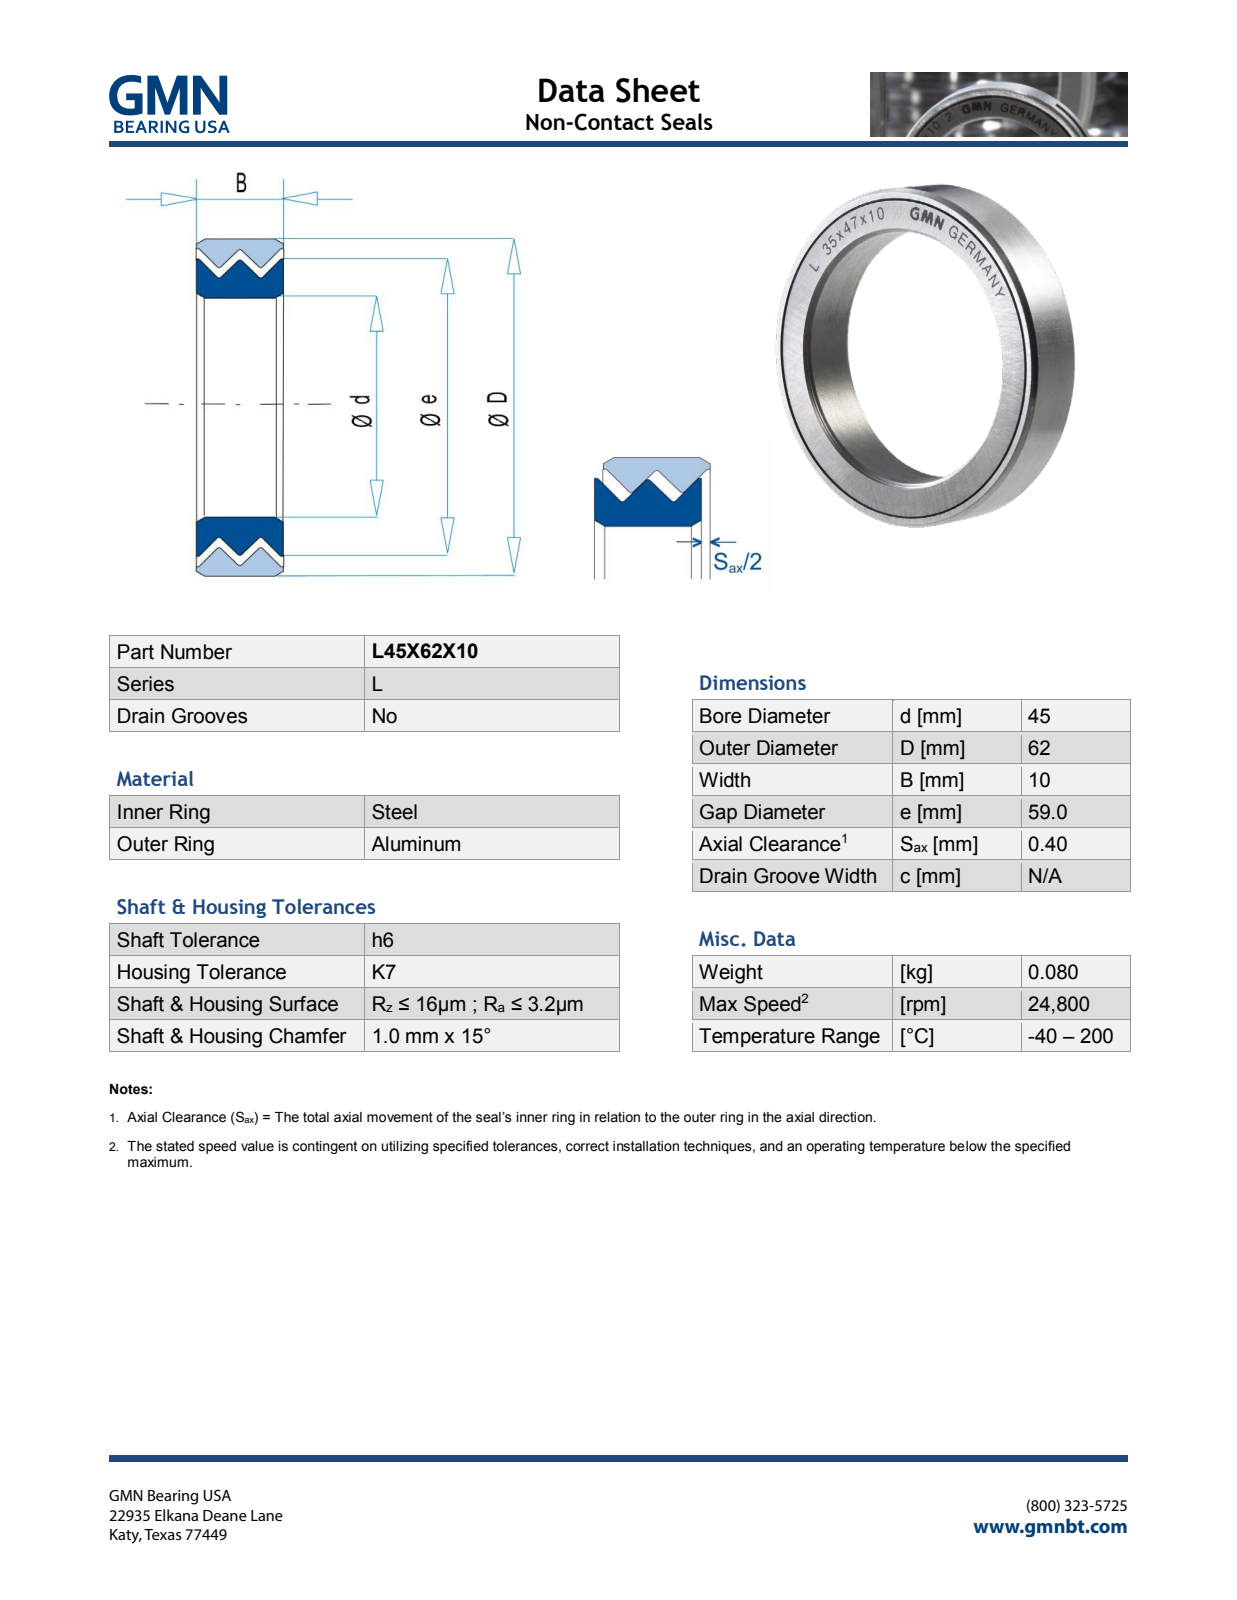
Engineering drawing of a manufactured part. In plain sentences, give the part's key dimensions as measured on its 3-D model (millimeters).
The part is named "L45X62X10_PRT". Its 3-D file was written by "PRO/ENGINEER BY PARAMETRIC TECHNOLOGY CORPORATION, 2013150 (AUTOMOTIVE_DESIGN)". It is 2 solids with 569 faces: 513 planar, 12 cylindrical and 44 other. Overall it measures 62 by 62 by 10.07 millimeters. Its volume is 13 763 cubic millimeters and its surface area 10 704 square millimeters. Round holes: 1 of diameter 45, 1 of diameter 59.28. Round bosses or shafts: 1 of diameter 62, 1 of diameter 59. The main face-to-face distances are 10, 10.07, 0.55, 0.56, 4.42, 3.87, 0.47, 3.13, 4.43, 3.86.
